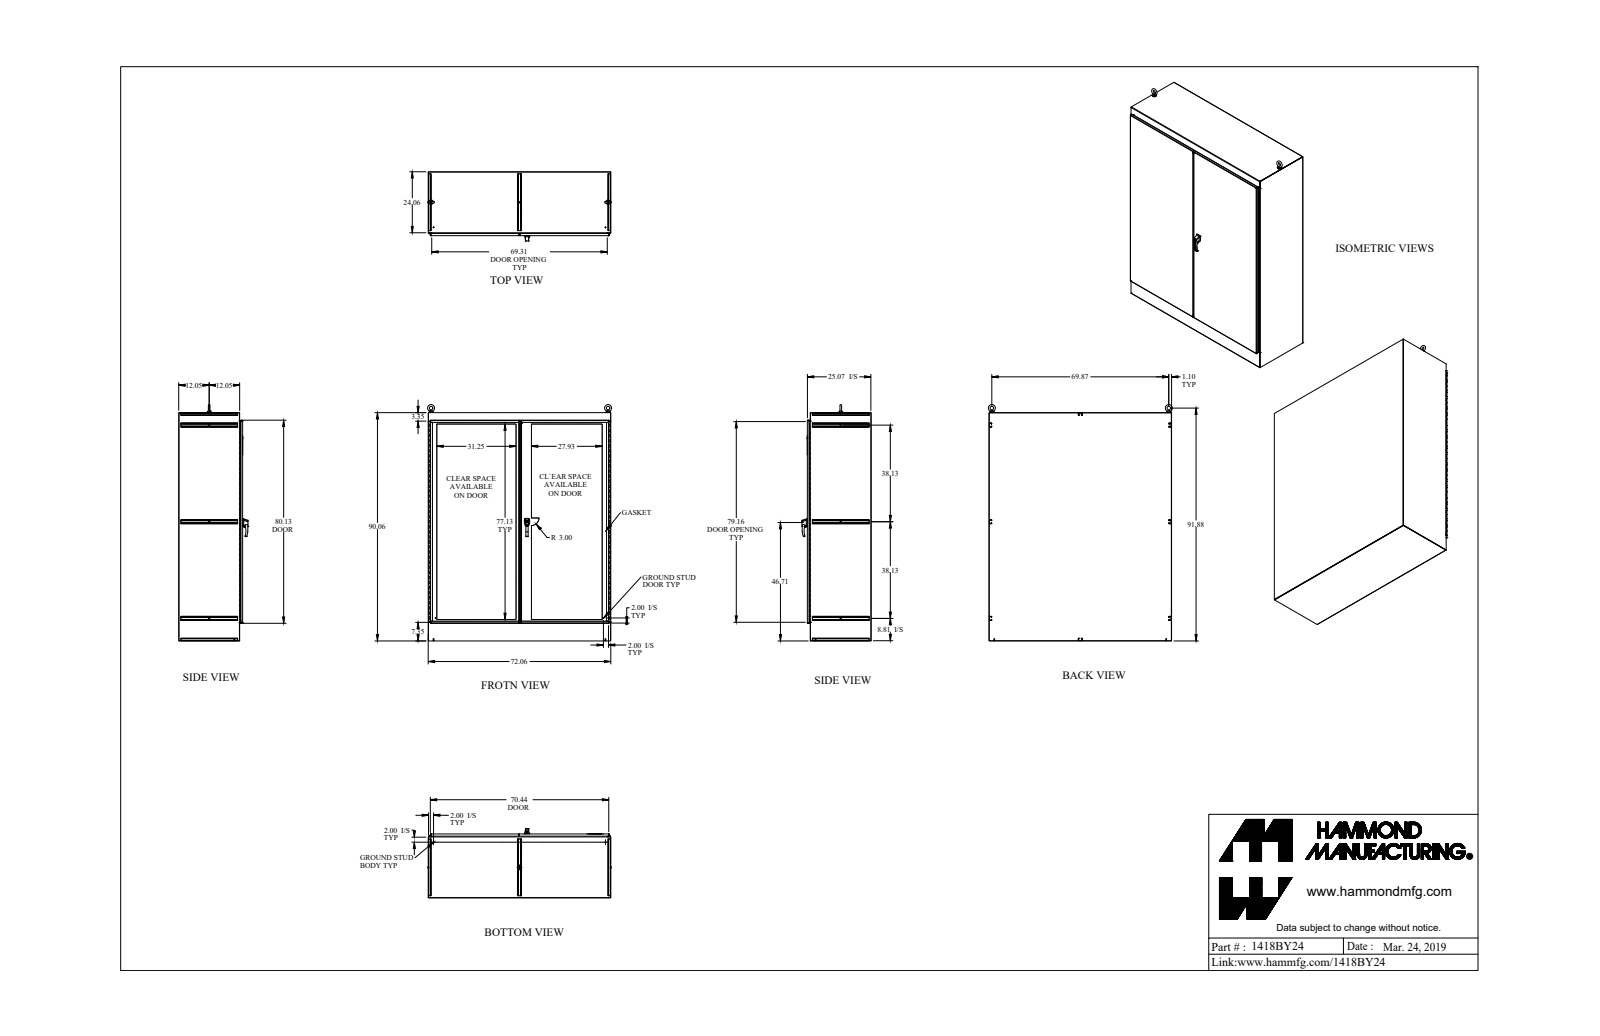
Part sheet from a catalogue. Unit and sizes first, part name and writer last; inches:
Units: inches
Overall size (bounding box): 93.713 × 73.118 × 27.337
Round holes (diameter × count): ⌀0.304 ×28, ⌀0.35 ×7, ⌀0.5 ×4, ⌀0.11 ×2, ⌀0.25 ×2, ⌀0.257 ×2, ⌀0.28 ×2, ⌀0.281 ×2, ⌀0.313 ×2, ⌀0.39 ×2, ⌀0.413 ×2, ⌀0.527 ×2
Round bosses / shafts (diameter × count): ⌀0.281 ×6, ⌀0.25 ×4, ⌀1.75 ×2, ⌀1.5 ×2, ⌀1.25 ×2, ⌀1 ×2, ⌀0.75 ×2, ⌀0.738 ×2
Partial cylindrical surfaces — rounded edges, fillets, slot ends (radius × count): R0.043 ×54, R0.138 ×48, R0.5 ×25, R0.125 ×22, R0.018 ×16, R0.06 ×15, R0.048 ×8, R0.05 ×8
Main face-to-face distances: 0.095, 0.125, 0.072, 25.096, 25.222, 25.024, 25.15, 71.965, 89.965, 71.87
Hole centre spacings: 6, 70.584, 12, 71.345, 18, 72.595, 24, 74.311
Volume: 2 375 in³ · Surface area: 48 634 in²
Bodies: 72 solids, 3268 faces (1887 planar, 1254 cylindrical, 127 other)
Part name (STEP PRODUCT): 1418BY24
STEP written by: SolidWorks 2019 (AUTOMOTIVE_DESIGN)
